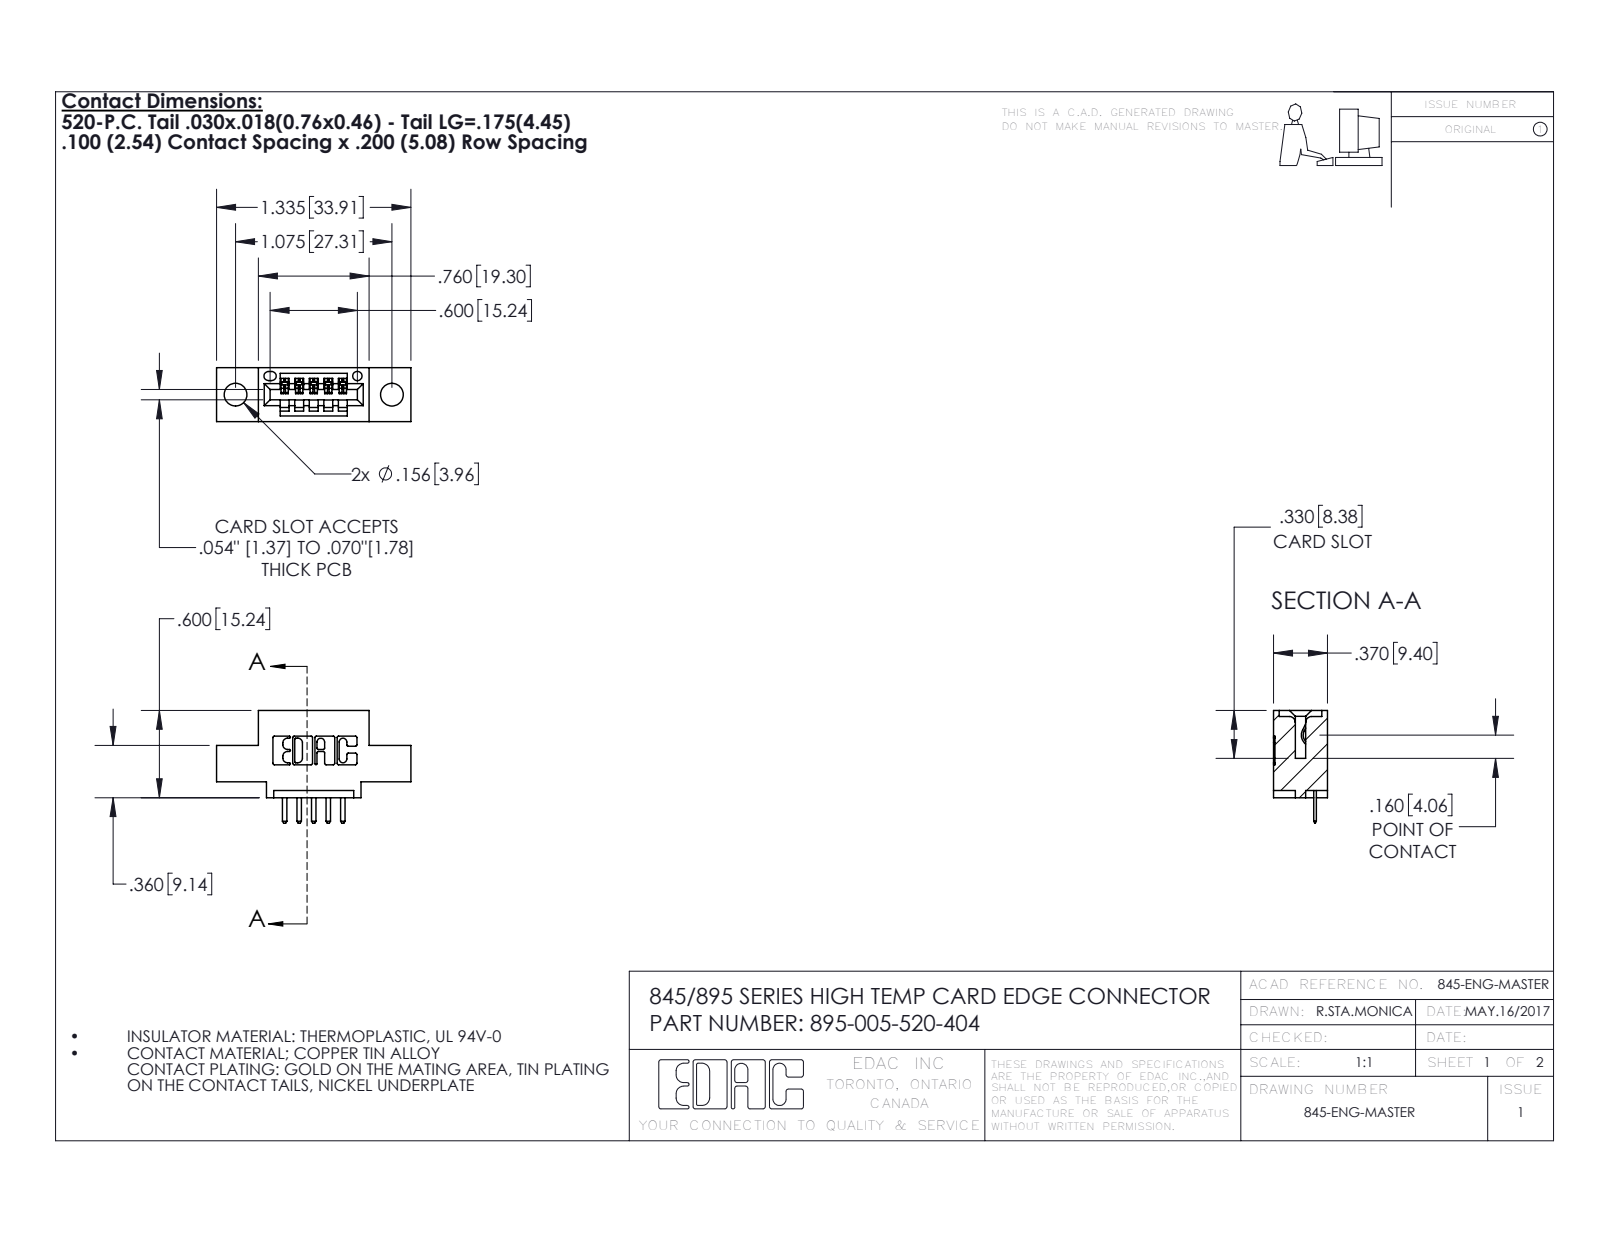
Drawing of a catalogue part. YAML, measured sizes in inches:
part_name: "345-292-001_345-293-120; 395-005-520-404; 345 Part_0.110 Offset - 0.156 Dia-TH"
step_written_by: "SolidWorks 2016 (CONFIG_CONTROL_DESIGN)"
units: inches
bodies: {solids: 6, faces: 440, planar: 294, cylindrical: 146, other: 0}
overall_size: [1.335, 0.775, 0.37]
volume: 0.167
surface_area: 4.626
round_holes:
  - {diameter: 0.156, count: 2}
  - {diameter: 0.064, count: 1}
partial_cylinders:
  - {radius: 0.01, count: 22}
  - {radius: 0.01, count: 12}
  - {radius: 0.006, count: 10}
  - {radius: 0.007, count: 6}
  - {radius: 0.031, count: 6}
  - {radius: 0.026, count: 3}
  - {radius: 0.031, count: 2}
  - {radius: 0.04, count: 2}
face_to_face_distances: [0.37, 0.2, 0.1, 0.298, 0.072, 0.25, 0.025, 0.06, 0.16, 0.55]
hole_center_spacings: [0.27, 0.847, 1.075]
